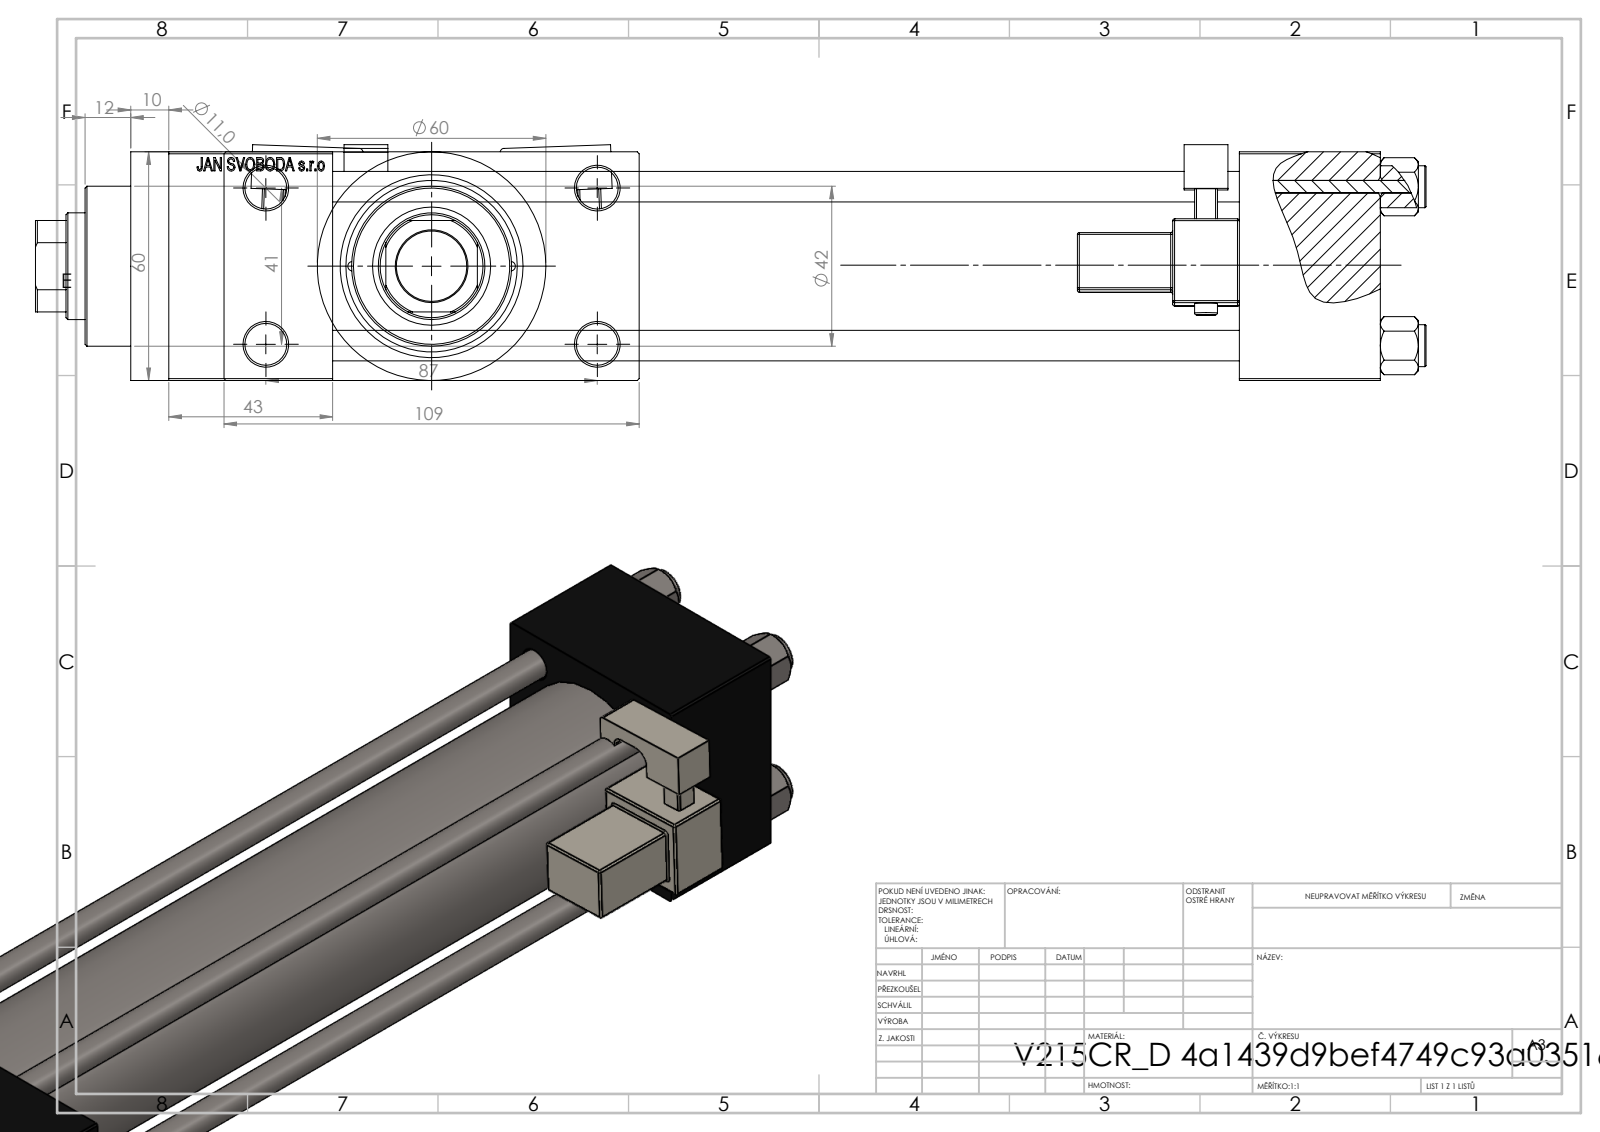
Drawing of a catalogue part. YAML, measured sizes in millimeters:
part_name: "V215CR_MSU; NUT_M5_D; V215_VC_A; V215CR_VCP_D (+2 more)"
step_written_by: "SolidWorks 2019 (CONFIG_CONTROL_DESIGN)"
units: millimeters
bodies: {solids: 13, faces: 1268, planar: 560, cylindrical: 152, other: 556}
overall_size: [365, 109, 61.9]
volume: 789475
surface_area: 223724
round_holes:
  - {diameter: 8, count: 4}
  - {diameter: 11, count: 4}
  - {diameter: 2.5, count: 2}
  - {diameter: 7, count: 2}
  - {diameter: 16.66, count: 2}
  - {diameter: 24, count: 2}
  - {diameter: 18.5, count: 1}
  - {diameter: 28, count: 1}
  - {diameter: 31, count: 1}
  - {diameter: 40, count: 1}
  - {diameter: 45, count: 1}
round_bosses_or_shafts:
  - {diameter: 11, count: 4}
  - {diameter: 6, count: 2}
  - {diameter: 60, count: 1}
  - {diameter: 46, count: 1}
  - {diameter: 42, count: 1}
partial_cylinders:
  - {radius: 0.5, count: 48}
  - {radius: 1, count: 2}
  - {radius: 2.5, count: 2}
  - {radius: 4, count: 2}
  - {radius: 13.5, count: 1}
face_to_face_distances: [60, 238, 24.5, 84.5, 37, 275, 318, 281, 43, 109]
hole_center_spacings: [20.85, 22.65, 29.49, 30.62, 41.7, 46.53, 47.15, 48.09]
